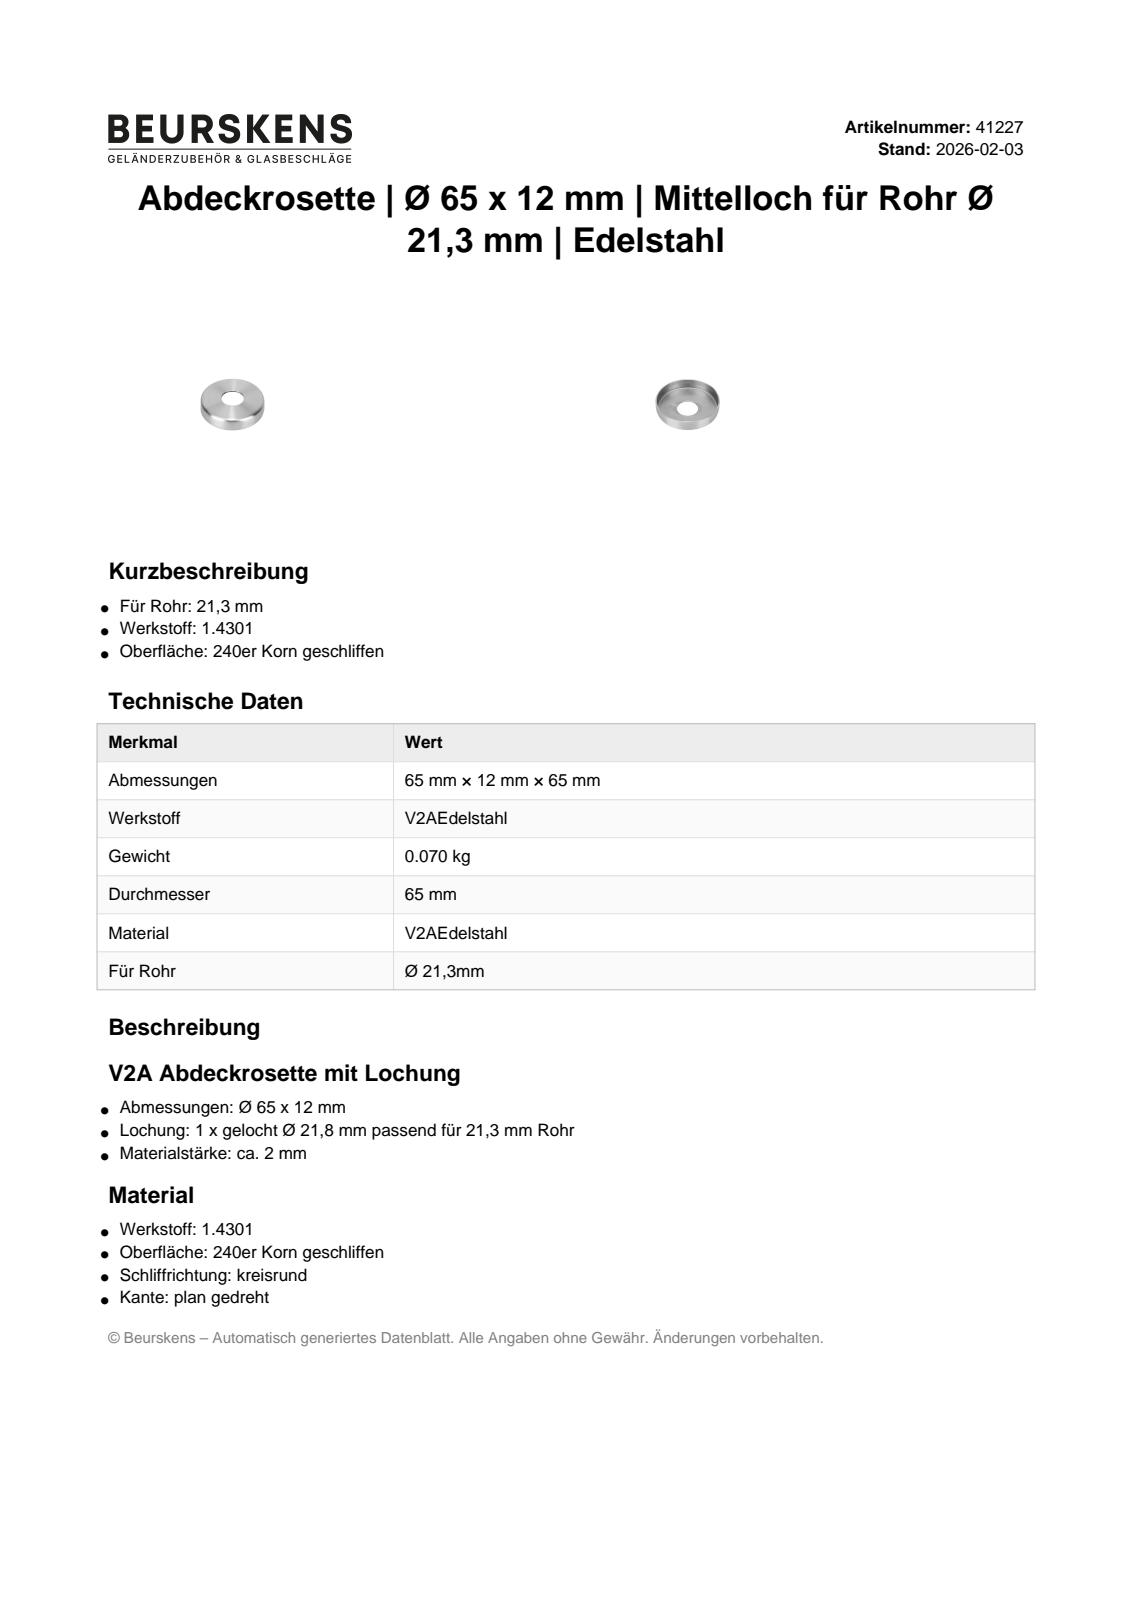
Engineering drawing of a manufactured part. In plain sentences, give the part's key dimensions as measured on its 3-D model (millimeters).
The part is named "41227". Its 3-D file was written by "Autodesk Inventor 2022 (AUTOMOTIVE_DESIGN)". It is 1 solid with 8 faces: 3 planar, 3 cylindrical and 2 other. Overall it measures 65 by 65 by 12 millimeters. Its volume is 9 503 cubic millimeters and its surface area 10 044 square millimeters. Round holes: 1 of diameter 21.8, 1 of diameter 61. Round bosses or shafts: 1 of diameter 65. The main face-to-face distances are 2, 10, 12.
